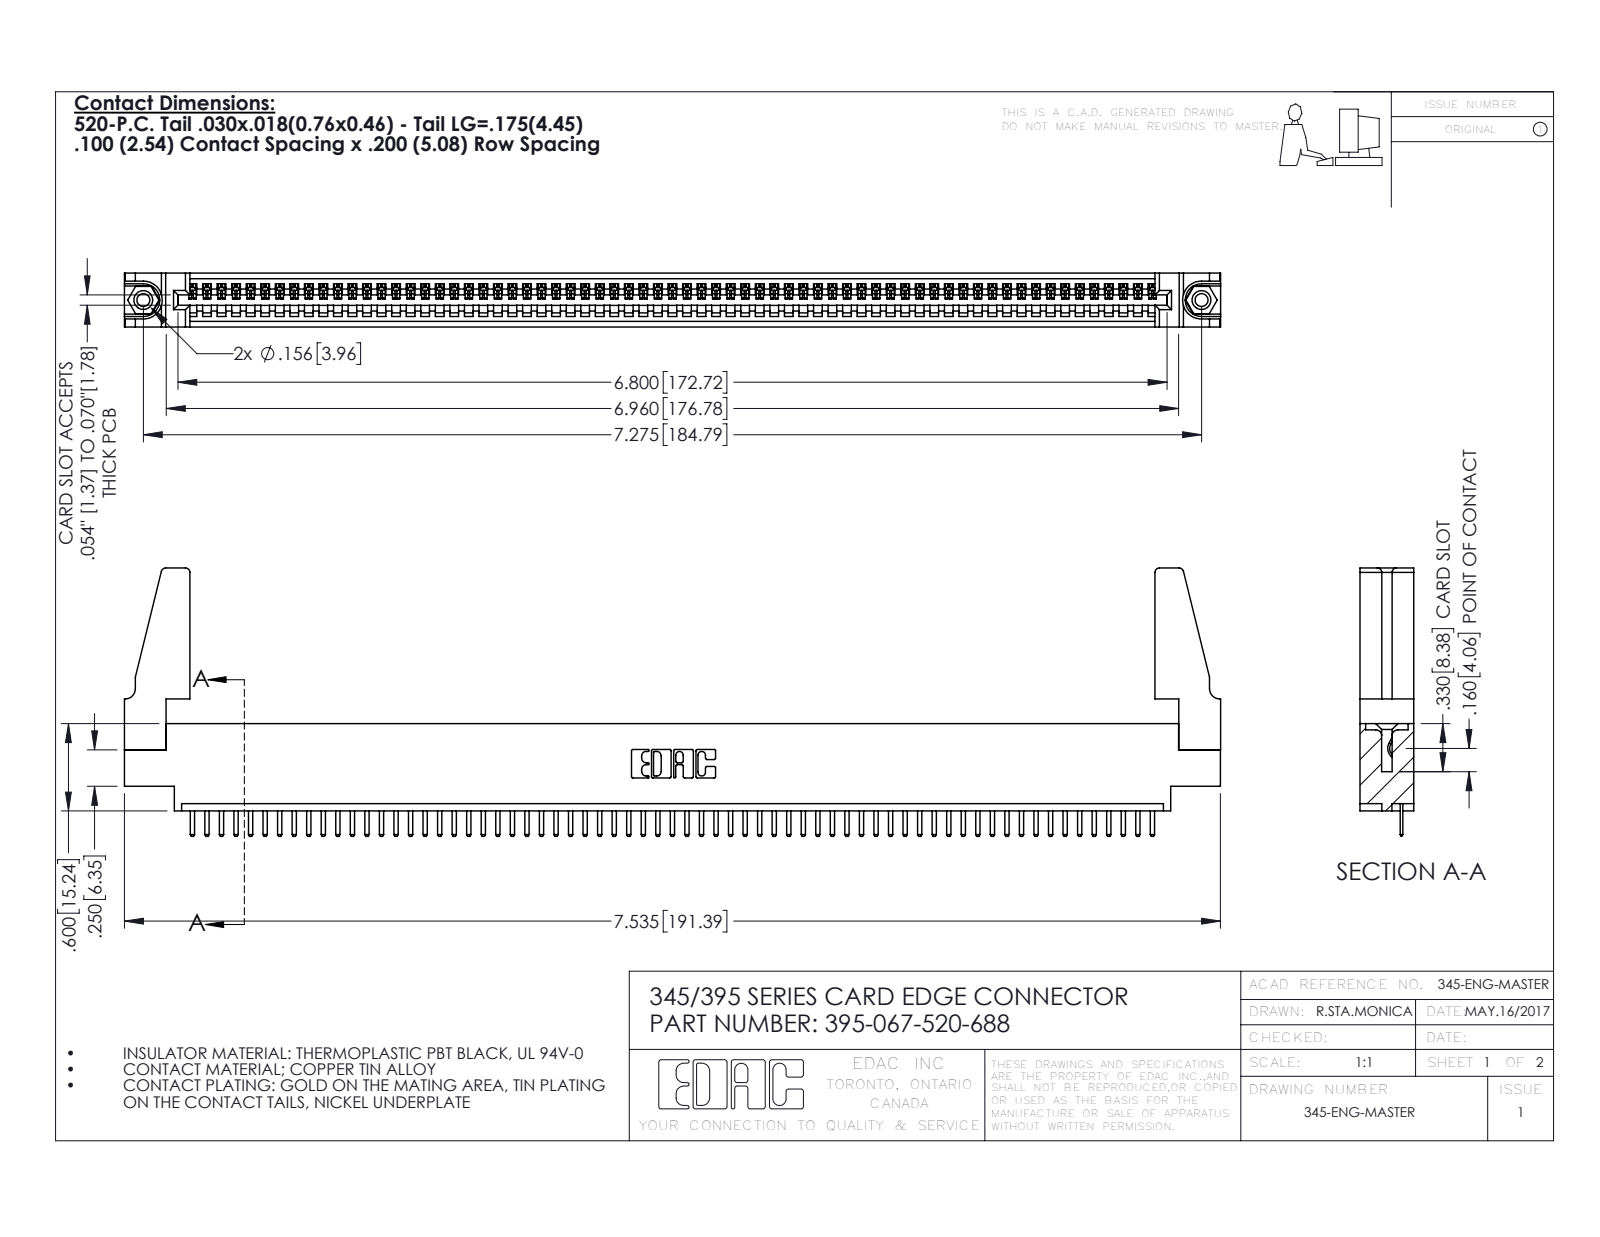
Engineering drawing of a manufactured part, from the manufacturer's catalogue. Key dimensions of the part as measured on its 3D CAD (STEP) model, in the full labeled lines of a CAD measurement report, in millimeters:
Part name (STEP PRODUCT): 395-067-520-688; 345-292-001_345-293-120; 345 Part_0.170 Offset - 0.156 Dia-TH; 345-220-078_345-220-088 (+1 more)
STEP written by: SolidWorks 2016 (CONFIG_CONTROL_DESIGN)
Units: millimetres
Bodies: 72 solids, 4408 faces (2970 planar, 1422 cylindrical, 16 other)
Overall size (bounding box): 191.4 × 46.9 × 9.4
Volume: 21 340 mm³ · Surface area: 26 990 mm²
Round holes (diameter × count): ⌀2.3 ×2, ⌀3.2 ×2, ⌀4 ×2, ⌀1.6 ×1
Round bosses / shafts (diameter × count): ⌀3.9 ×2
Partial cylindrical surfaces — rounded edges, fillets, slot ends (radius × count): R0.3 ×136, R0.2 ×134, R0.3 ×22, R0.8 ×8, R0.2 ×6, R0.8 ×6, R0.7 ×3, R0.8 ×2
Main face-to-face distances: 1.8, 7.6, 9.4, 2.5, 6.9, 0.6, 5.1, 5.7, 1.8, 4.4
Hole centre spacings: 6.9, 178.8, 184.8
